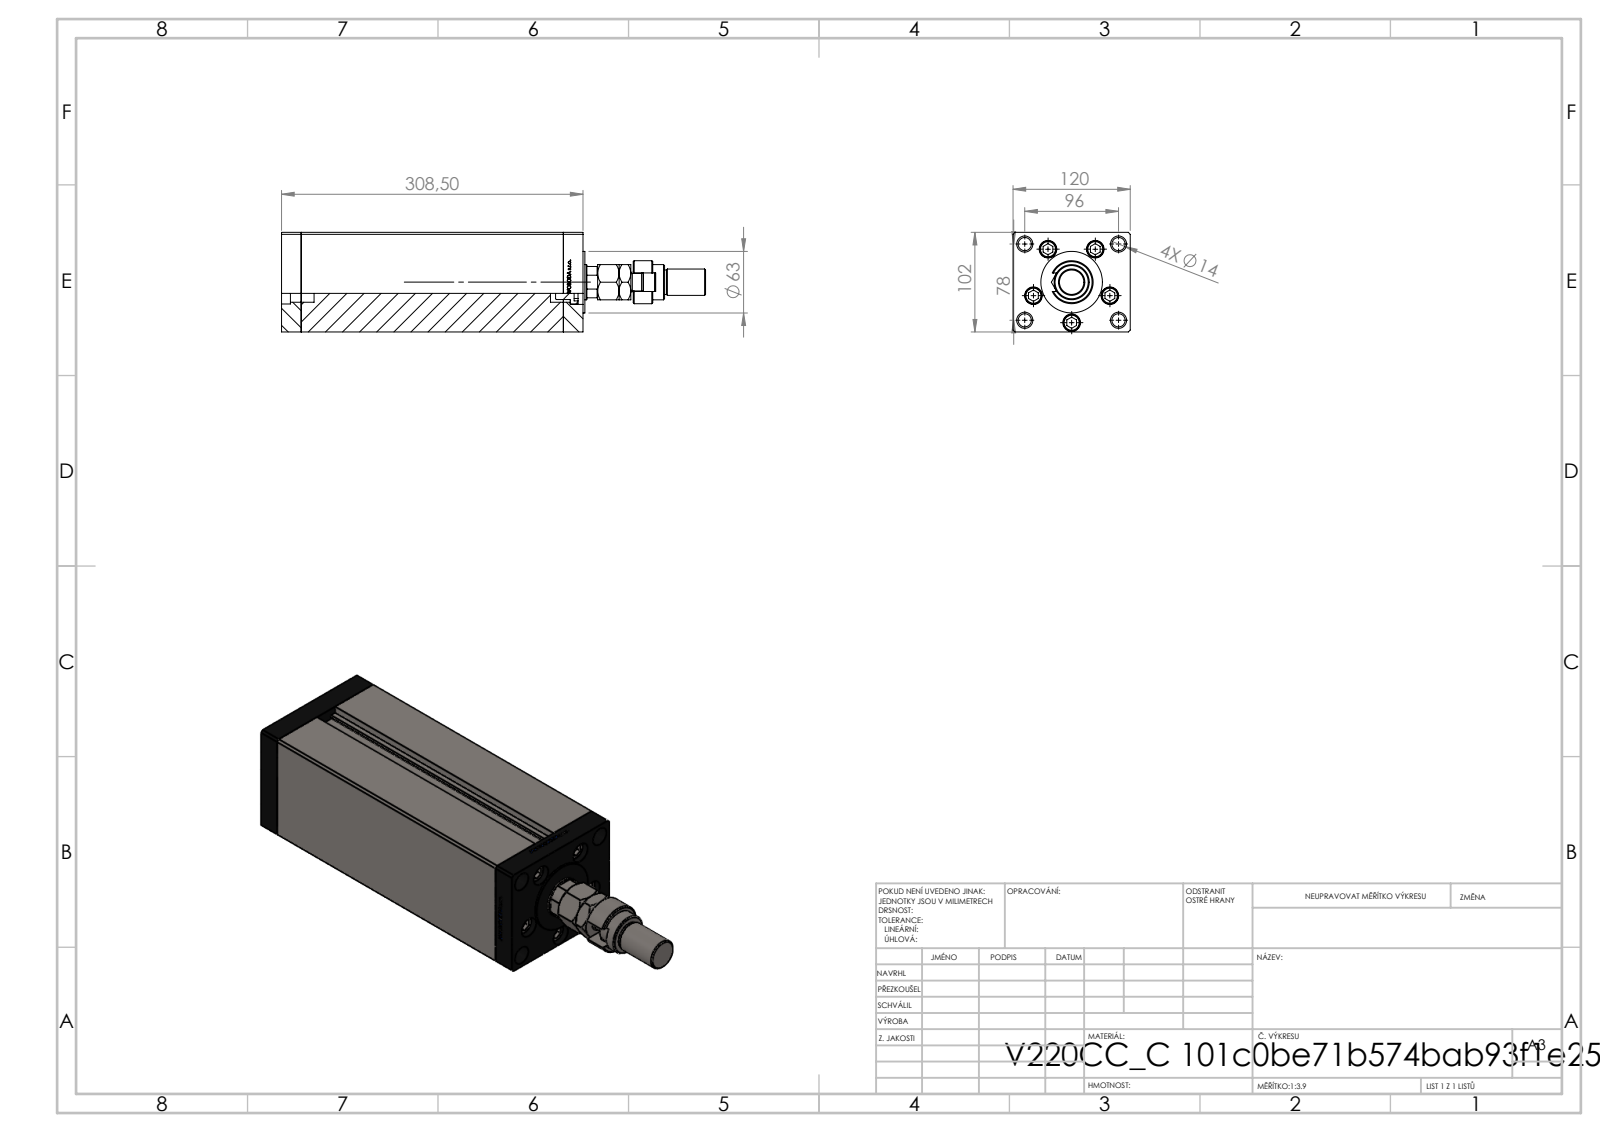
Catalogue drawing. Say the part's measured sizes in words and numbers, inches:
The part is named "ALLEN BOLT; V220C BACK_C; V220C_C MIDDLE; FEMALE_PART_FOR_DFA (+3 more)". Its 3-D file was written by "SolidWorks 2019 (CONFIG_CONTROL_DESIGN)". It is 15 solids with 1250 faces: 570 planar, 174 cylindrical and 506 other. Overall it measures 17.087 by 4.724 by 4.016 inches. Its volume is 197.4 cubic inches and its surface area 615.4 square inches. Round holes: 9 of diameter 0.531, 5 of diameter 0.709, 4 of diameter 0.472, 4 of diameter 0.65, 1 of diameter 0.669, 1 of diameter 1.004. Round bosses or shafts: 5 of diameter 0.315, 4 of diameter 0.669, 1 of diameter 2.48, 1 of diameter 1.732, 1 of diameter 1.417, 1 of diameter 1.102, 1 of diameter 1.063, 1 of diameter 0.984. Partial cylindrical surfaces (rounded edges, fillets, slot ends): 2 of radius 0.037, 1 of radius 0.374, 1 of radius 0.591, 1 of radius 0.689. The main face-to-face distances are 4.724, 4.016, 0.787, 10.571, 11.358, 1.348, 12.146, 10.797, 10.01, 0.561. The hole center spacings are 1.634, 2.435, 0.96, 1.051, 1.887, 1.893, 1.962, 2.109.
